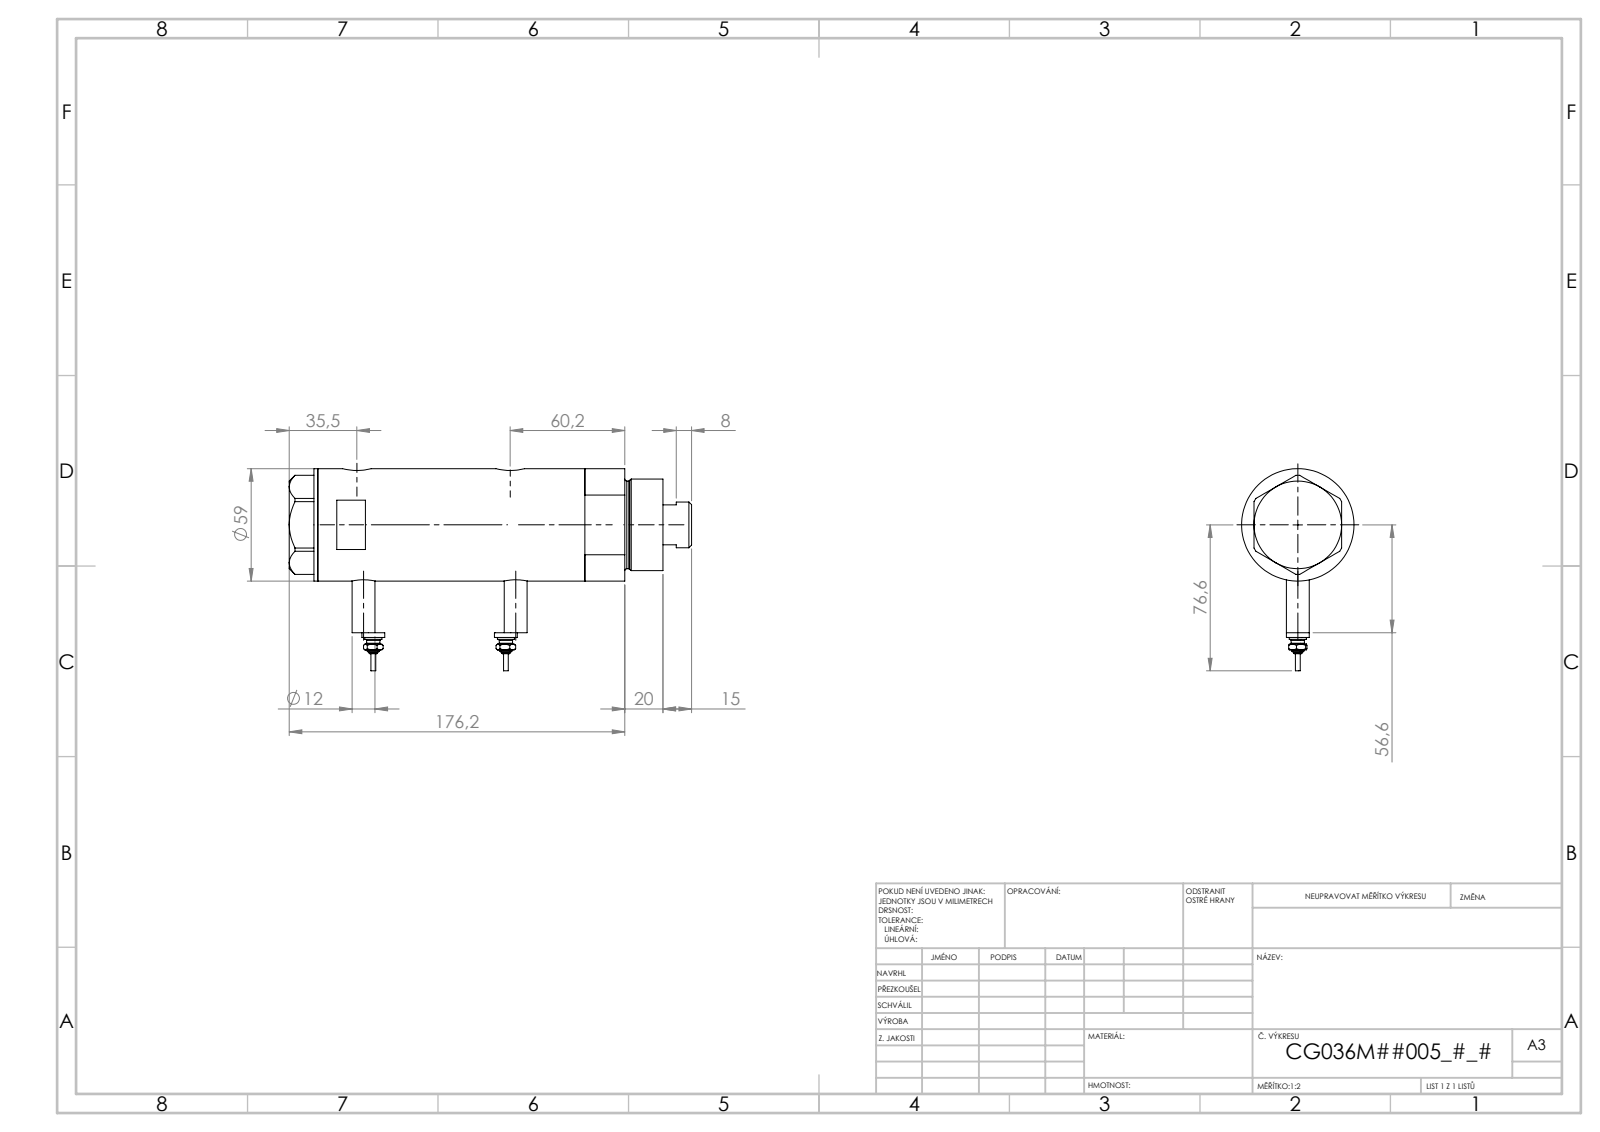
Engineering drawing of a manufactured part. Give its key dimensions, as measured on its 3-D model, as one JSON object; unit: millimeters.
{"part_name": "V270CG_SWITCH; V270CG_MIDDLE; V270CG_BACK; V270CG_VC (+1 more)", "step_written_by": "SolidWorks 2019 (CONFIG_CONTROL_DESIGN)", "units": "millimeters", "bodies": {"solids": 6, "faces": 232, "planar": 81, "cylindrical": 77, "other": 74}, "overall_size": [168.42, 91.3, 59], "volume_mm3": 385033, "surface_area_mm2": 85725, "round_holes": [[5, 2], [9.73, 2], [12.5, 2], [15, 2], [8.5, 1], [25, 1], [26.5, 1], [36, 1], [40, 1], [52, 1]], "round_bosses_or_shafts": [[12, 3], [9, 2], [7, 2], [4.34, 2], [2.4, 2], [59, 1], [48, 1], [46, 1]], "face_to_face_distances": [62.34, 23.5, 38.84, 15, 38.5, 77.34, 153.42, 138.42, 114.92, 76.08], "hole_center_spacings": [2.9, 3.5, 37.15, 40.05, 40.65, 43.55, 2.89, 2.91]}
